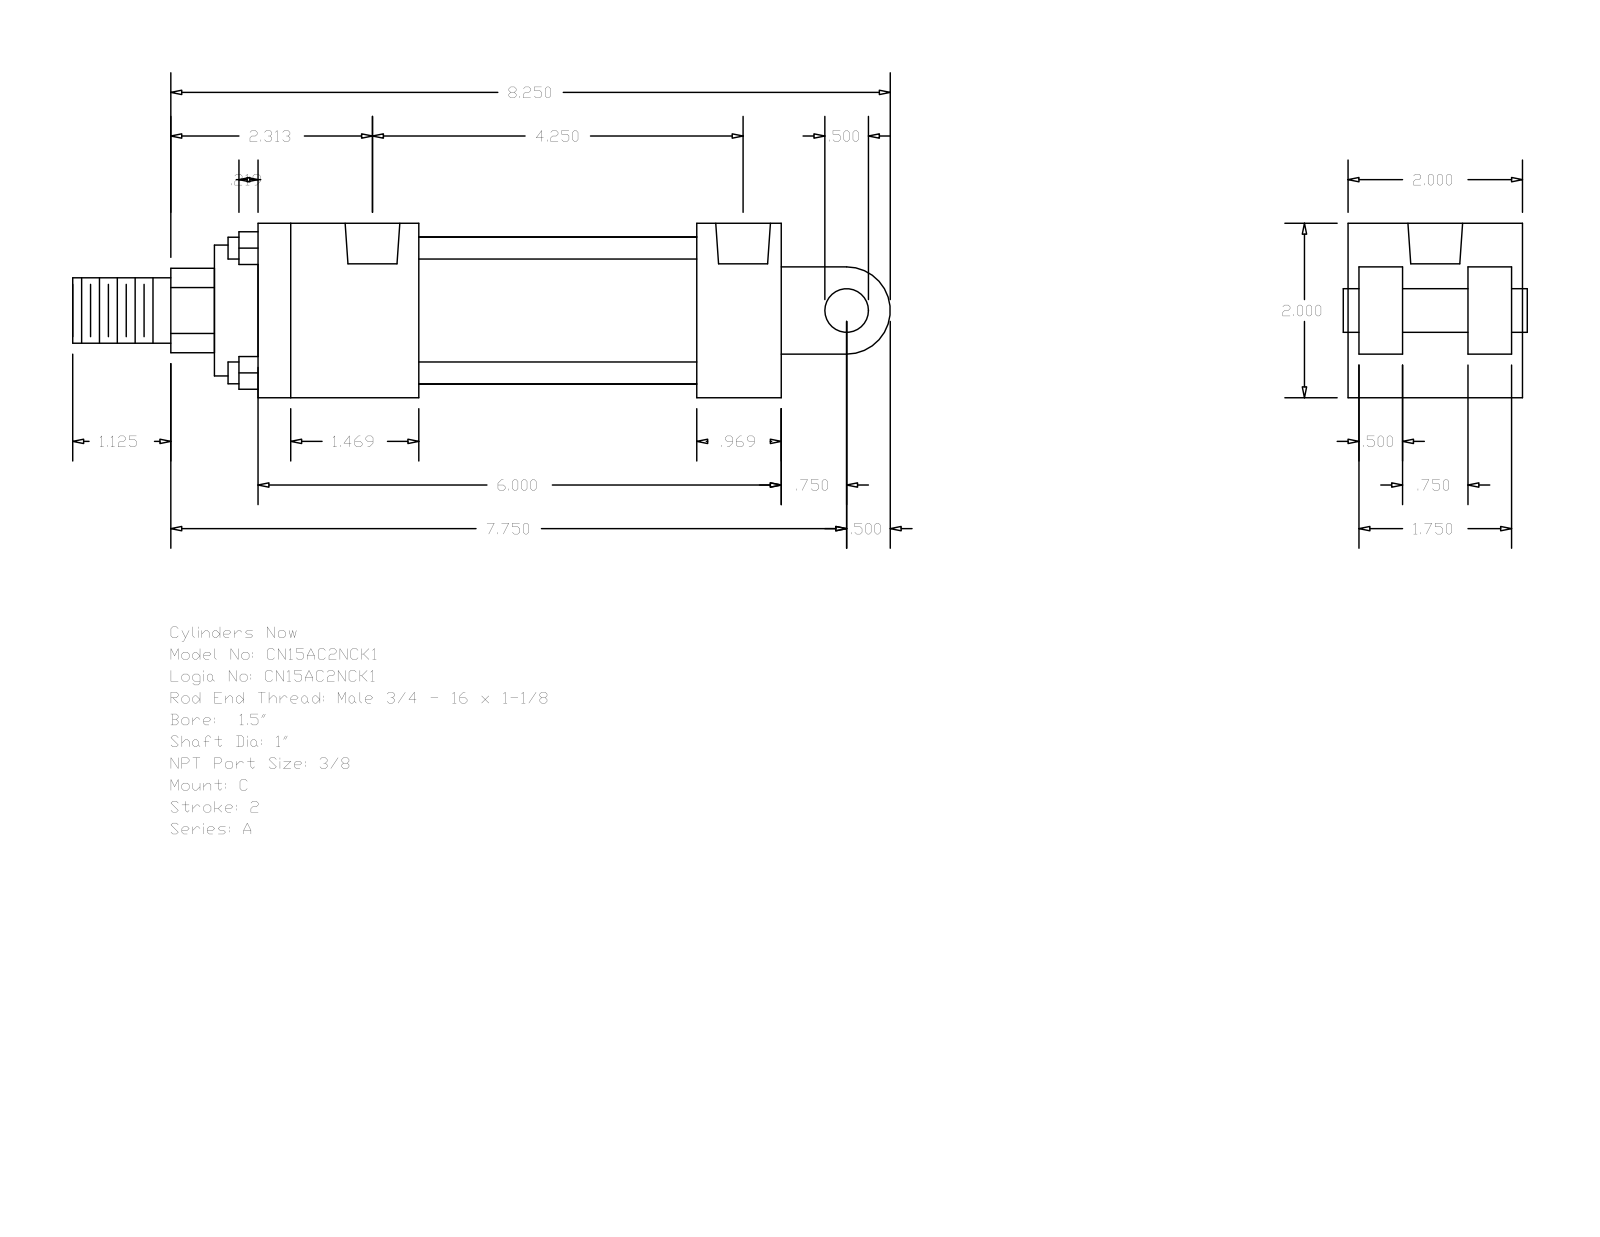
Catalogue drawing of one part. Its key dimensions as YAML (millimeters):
part_name: "A_C__0150_1"
step_written_by: "GSSL Pune (CONFIG_CONTROL_DESIGN)"
units: millimeters
bodies: {solids: 0, faces: 99, planar: 70, cylindrical: 29, other: 0}
overall_size: [238.12, 50.8, 50.8]
round_holes:
  - {diameter: 5.56, count: 4}
  - {diameter: 15.93, count: 2}
round_bosses_or_shafts:
  - {diameter: 6.35, count: 4}
  - {diameter: 42.93, count: 1}
  - {diameter: 38.1, count: 1}
  - {diameter: 25.4, count: 1}
  - {diameter: 19.05, count: 1}
  - {diameter: 12.7, count: 1}
partial_cylinders:
  - {radius: 12.29, count: 1}
  - {radius: 12.7, count: 1}
face_to_face_distances: [50.8, 12.7, 3.17, 15.87, 47.63, 34.93, 31.76, 152.4, 38.1, 127.79]
hole_center_spacings: [3.97, 100.01, 103.98, 107.95]
